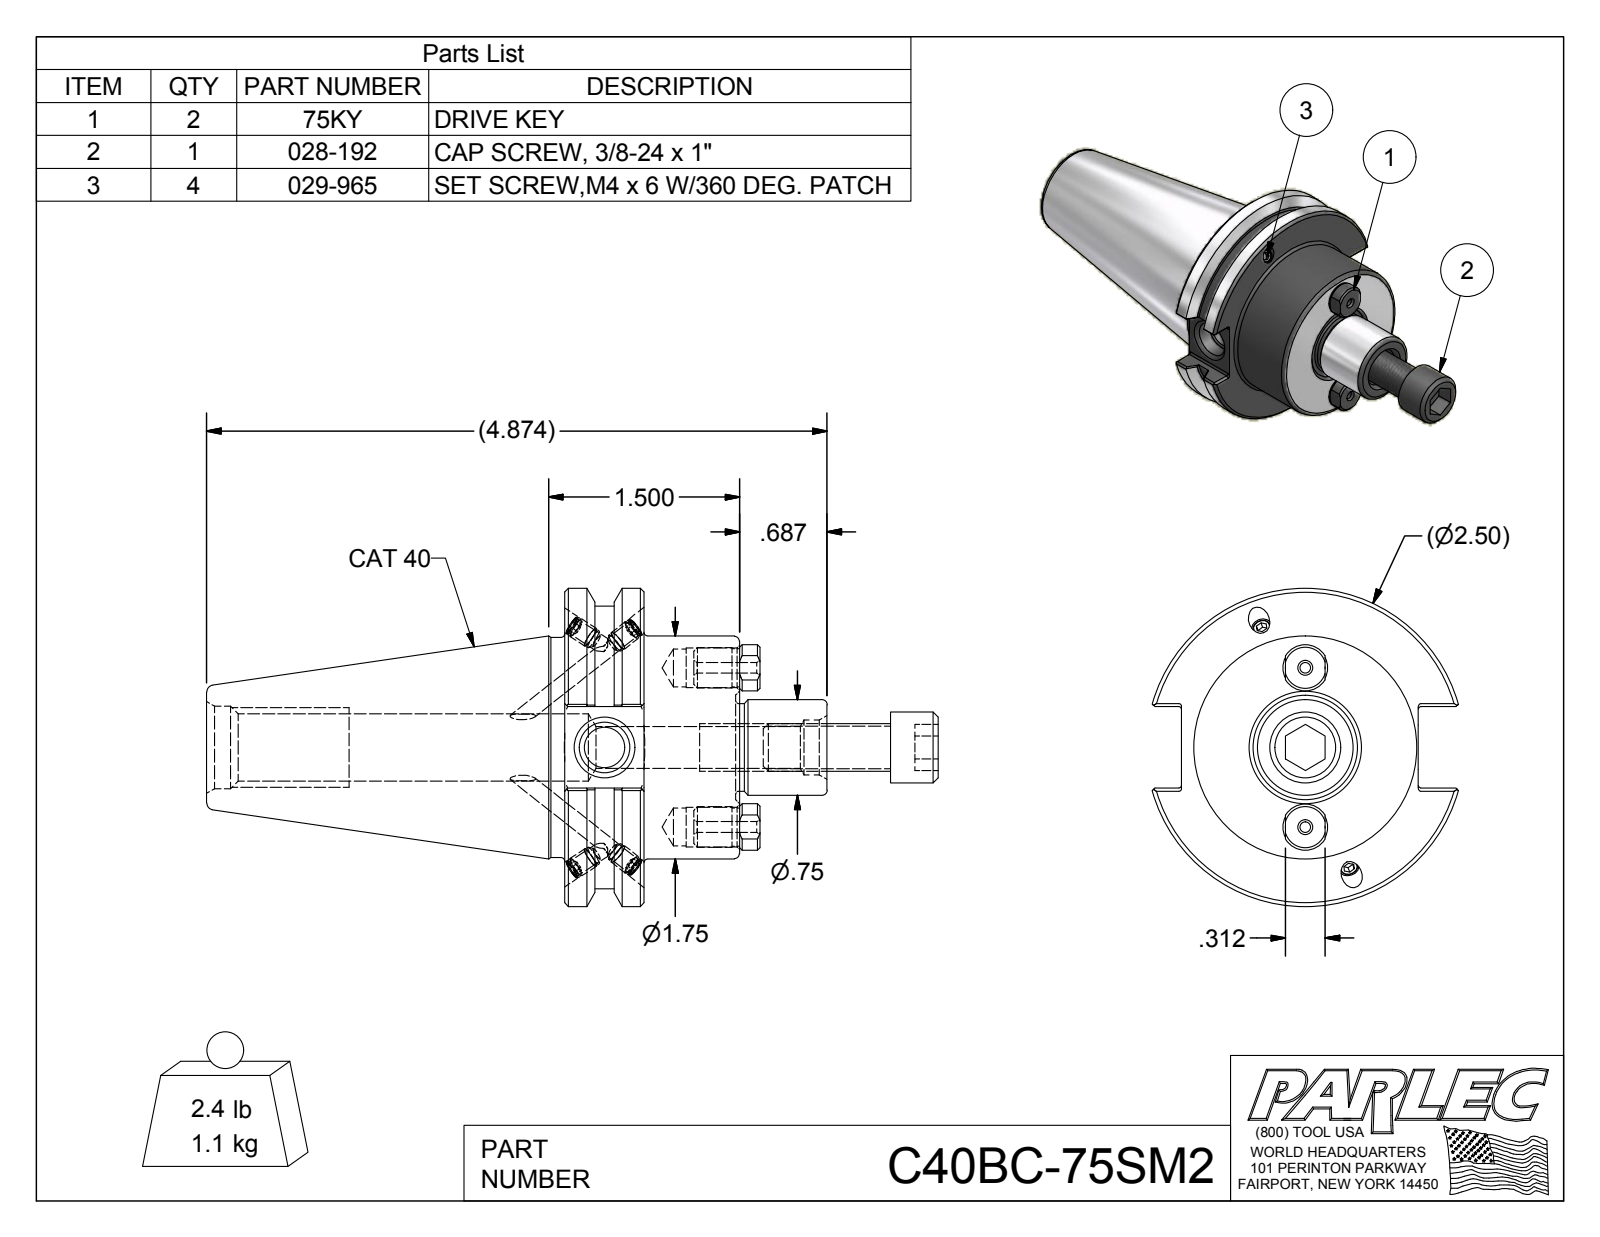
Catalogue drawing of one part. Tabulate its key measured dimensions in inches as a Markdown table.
| quantity | value |
| --- | --- |
| part name | C40BC-75SM2; C40BC-75SM2-1; 75KY; 028-192 (+1 more) |
| STEP written by | Autodesk Inventor 2012 (AUTOMOTIVE_DESIGN) |
| units | inches |
| bodies | 8 solids, 234 faces (101 planar, 64 cylindrical, 69 other) |
| overall size | 5.746 × 2.5 × 2.406 |
| volume | 8.29 in³ |
| surface area | 45.42 in² |
| round holes (diameter × count) | 0.13 × 4, 0.161 × 4, 0.084 × 2, 0.297 × 2, 0.312 × 2, 0.315 × 1, 0.33 × 1, 0.399 × 1, 0.43 × 1, 0.527 × 1, 0.648 × 1 |
| round bosses / shafts (diameter × count) | 0.165 × 4, 0.157 × 4, 0.318 × 2, 0.3 × 2, 2.5 × 1, 2.219 × 1, 1.75 × 1, 1.73 × 1 |
| partial cylindrical surfaces (radius × count) | 0.02 × 12, 0.183 × 2 |
| main face-to-face distances | 0.625, 1.375, 0.75, 0.64, 0.5, 1.86, 2.812, 3.437, 4.187, 3.201 |
| hole center spacings | 0.625, 1.25 |
